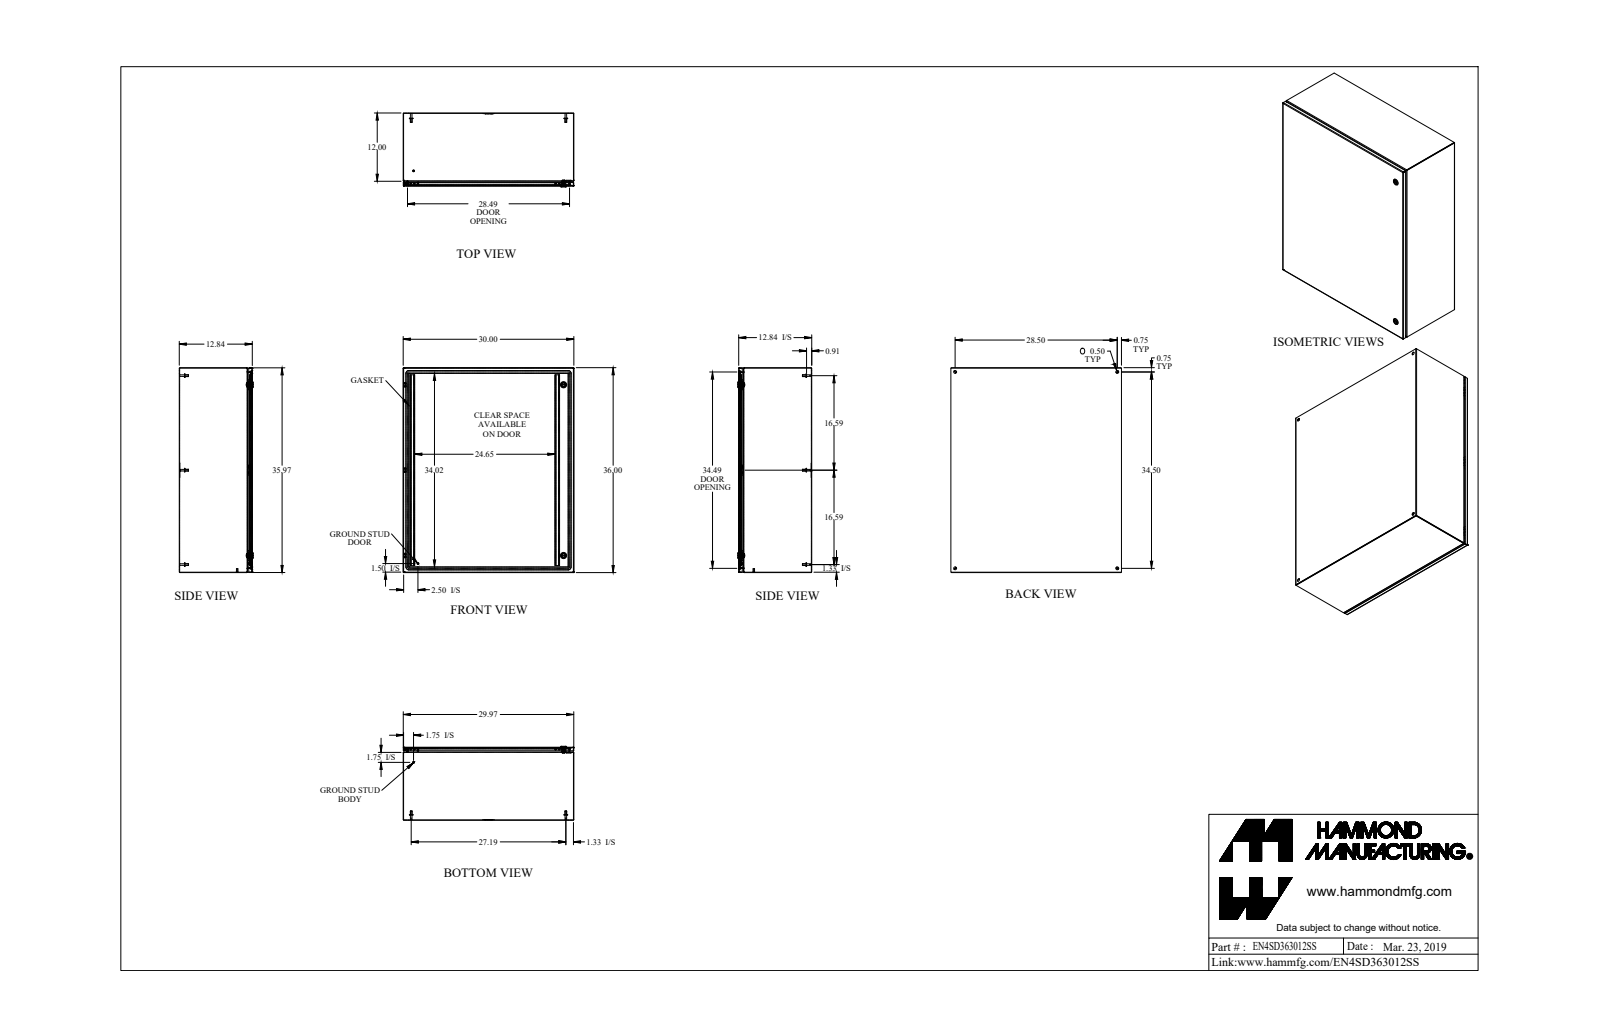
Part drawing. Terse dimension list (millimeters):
name: EN4SD363012SS
written by: SolidWorks 2019 (AUTOMOTIVE_DESIGN)
unit: mm
bodies: 37 solids, 943 faces (454 planar, 309 cylindrical, 180 other)
size: 914.4 × 762 × 330.3
volume: 5 003 000 mm³; area: 5 526 000 mm²
holes: 6× ⌀12.7, 2× ⌀5, 2× ⌀9.8, 2× ⌀16, 2× ⌀19.5, 1× ⌀4.4, 1× ⌀6.1, 1× ⌀6.1
bosses: 8× ⌀15.9, 8× ⌀8, 6× ⌀7, 2× ⌀27.9, 2× ⌀19.9, 2× ⌀13.3, 2× ⌀6.4, 2× ⌀6
rounds: 18× R0.9, 18× R2.7, 12× R0.3, 12× R1.2, 12× R7.9, 6× R0.2, 6× R1.6, 4× R3.2
face distances: 1.8, 324.4, 322.5, 326.2, 760.2, 912.6, 758.3, 762, 910.7, 914.4
hole spacings: 699.3, 723.9, 876.3, 1136.6, 63.2, 63.2, 762, 819.6
